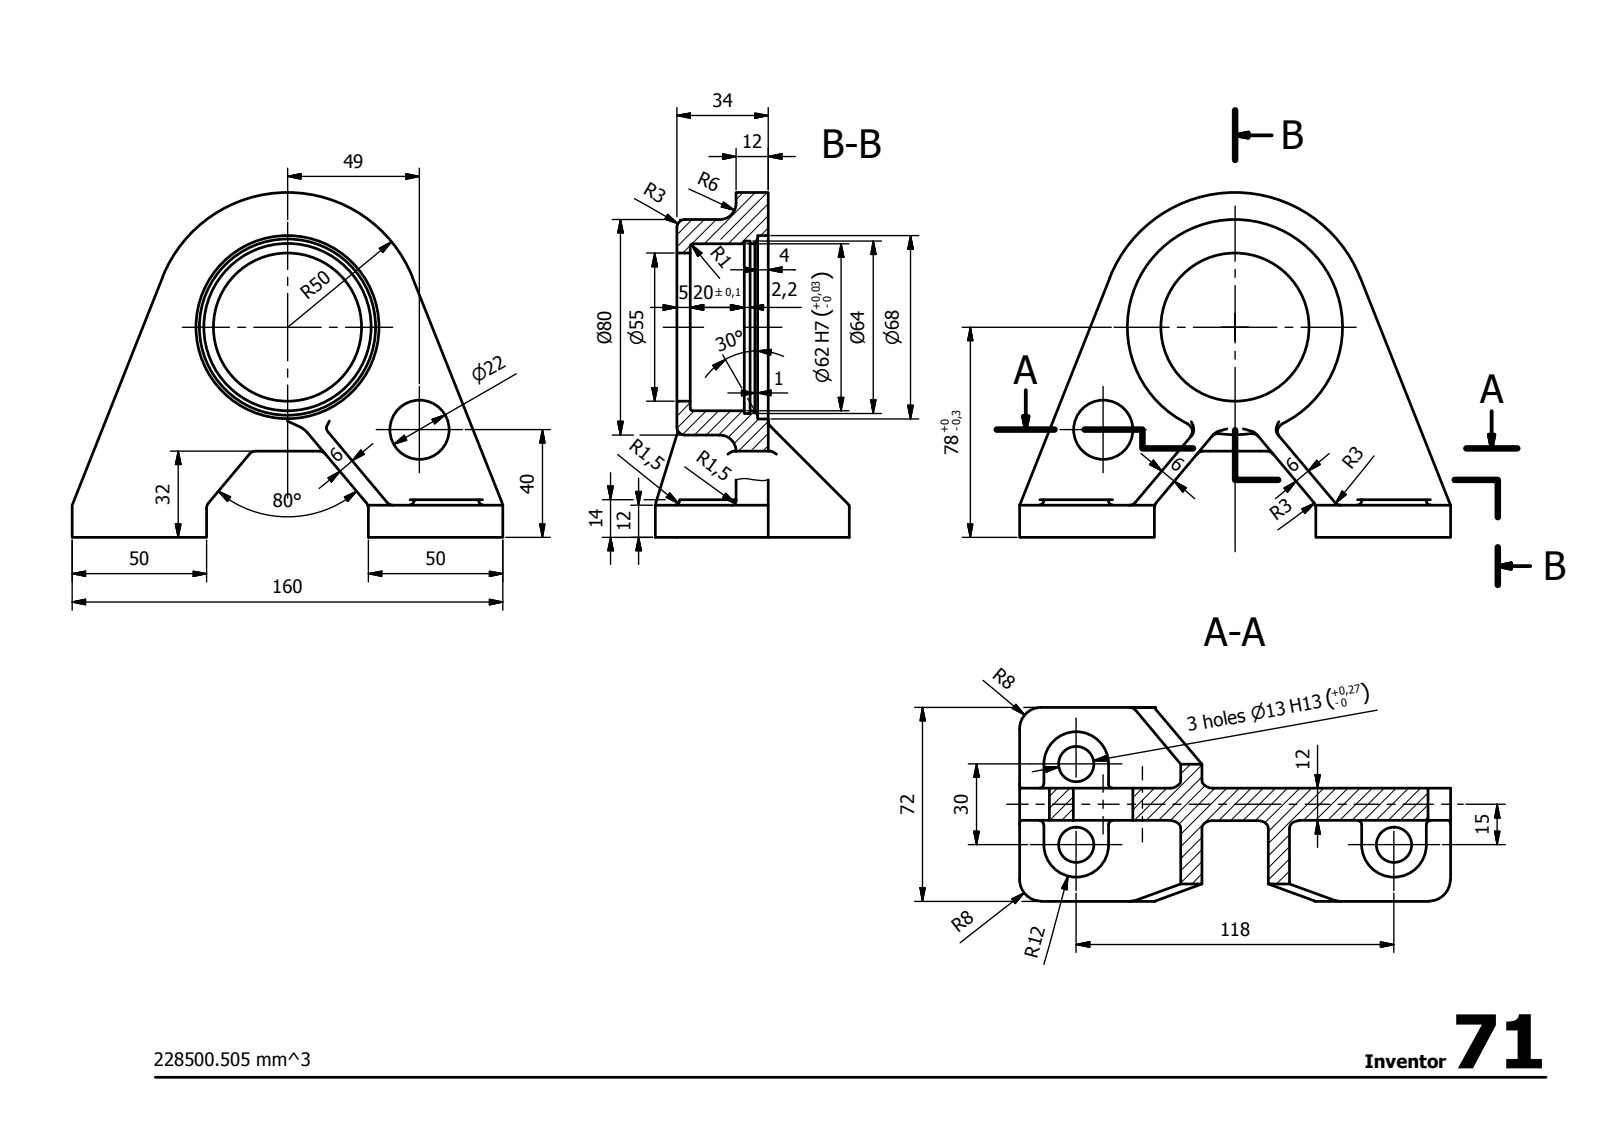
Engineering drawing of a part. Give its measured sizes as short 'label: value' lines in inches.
written by: Autodesk Inventor 2014 (AUTOMOTIVE_DESIGN)
unit: in
bodies: 1 solid, 125 faces (41 planar, 54 cylindrical, 30 other)
size: 6.299 × 5.039 × 2.835
volume: 13.94 in³; area: 85.12 in²
holes: 3× ⌀0.512, 1× ⌀0.866, 1× ⌀2.165, 1× ⌀2.441, 1× ⌀2.52, 1× ⌀2.677
bosses: 1× ⌀3.15
rounds: 17× R0.118, 12× R0.059, 3× R0.315, 3× R0.472, 1× R1.969
face distances: 0.472, 1.339, 0.866, 1.181, 1.654, 0.315, 0.237, 1.969, 0.551, 0.079
hole spacings: 1.181, 2.441, 4.646, 4.793
